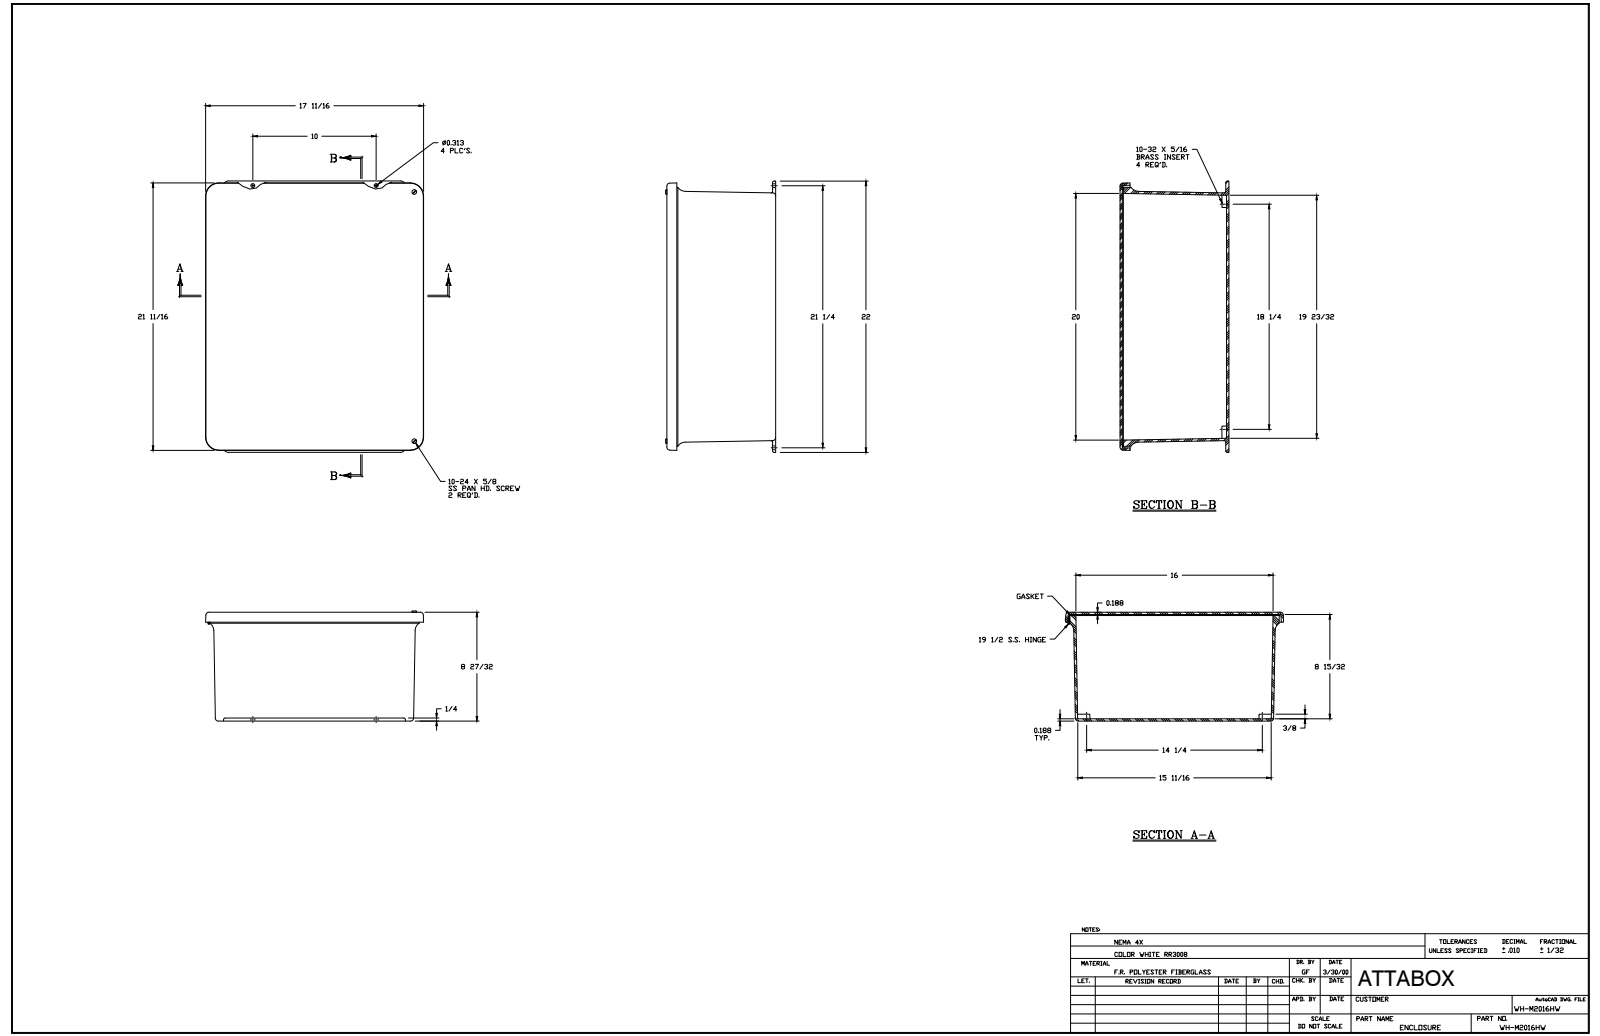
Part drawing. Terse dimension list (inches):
name: WH-M2016HW
written by: SolidWorks 2018 (AUTOMOTIVE_DESIGN)
unit: in
bodies: 26 solids, 977 faces (393 planar, 383 cylindrical, 201 other)
size: 22 × 17.711 × 8.96
volume: 282.9 in³; area: 2 939 in²
holes: 12× ⌀0.131, 12× ⌀0.14, 5× ⌀0.152, 4× ⌀0.156, 4× ⌀0.218, 2× ⌀0.145, 1× ⌀0.085
bosses: 12× ⌀0.25, 7× ⌀0.125, 6× ⌀0.27, 5× ⌀0.125, 2× ⌀0.19, 2× ⌀0.156, 1× ⌀0.155, 1× ⌀0.155
rounds: 20× R0.031, 10× R0.125, 8× R0.25, 5× R0.2, 4× R0.062, 4× R0.375, 4× R0.75
face distances: 0.187, 8.642, 8.829, 0.188, 8.454, 8.641, 0.313, 0.5, 8.563, 8.375
hole spacings: 3.75, 7.5, 0.25, 3.5, 4, 7.25, 7.75, 11
